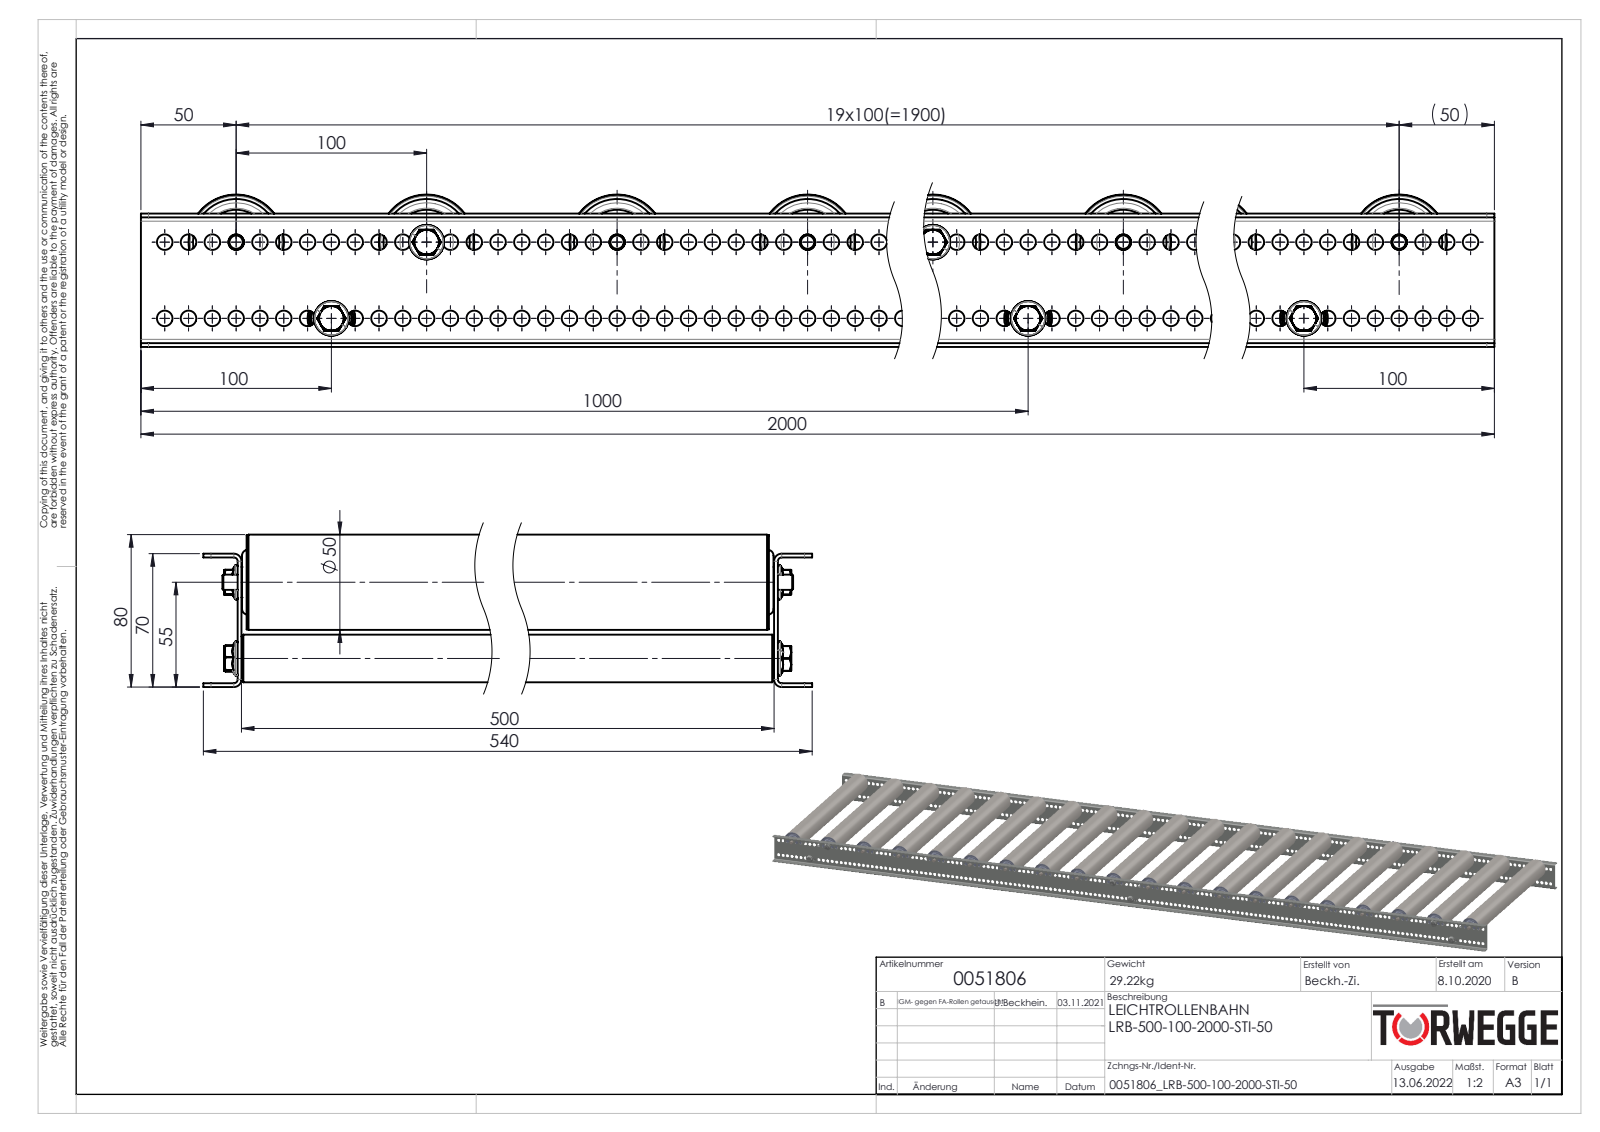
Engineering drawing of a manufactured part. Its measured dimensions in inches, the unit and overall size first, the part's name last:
Units: inches
Overall size (bounding box): 78.74 × 21.26 × 3.15
Round holes (diameter × count): ⌀0.323 ×318, ⌀0.673 ×20, ⌀0.728 ×20, ⌀1.091 ×20, ⌀1.783 ×20, ⌀1.85 ×20, ⌀0.299 ×17, ⌀0.268 ×6, ⌀0.472 ×3, ⌀0.48 ×3, ⌀0.756 ×3, ⌀0.827 ×3
Round bosses / shafts (diameter × count): ⌀0.315 ×23, ⌀1.969 ×20, ⌀1.949 ×20, ⌀1.862 ×20, ⌀1.169 ×20, ⌀1.079 ×20, ⌀1.075 ×20, ⌀0.63 ×20
Partial cylindrical surfaces — rounded edges, fillets, slot ends (radius × count): R0.024 ×34, R0.03 ×34, R0.096 ×34, R0.192 ×17, R0.276 ×17, R0.098 ×12, R0.157 ×8, R0.079 ×4
Main face-to-face distances: 0.079, 19.764, 2.677, 19.685, 19.843, 2.756, 2.598, 0.039, 0.091, 19.752
Hole centre spacings: 0.492, 0.984, 1.476, 1.969, 2.461, 2.953, 3.445, 3.937
Volume: 258.9 in³ · Surface area: 7 618 in²
Bodies: 476 solids, 8806 faces (1716 planar, 3328 cylindrical, 3762 other)
Part name (STEP PRODUCT): Tragrollenachse-Ø8_KFG_L=520; 0024178_Passscheibe_DIN988_12x18x1; Druckfeder_1,2x10x30; Sicherungsring_DIN471_8x0.8_Circlip DIN 471 - 8 x 0.8 (+8 more)
STEP written by: SolidWorks 2020 (AUTOMOTIVE_DESIGN)
